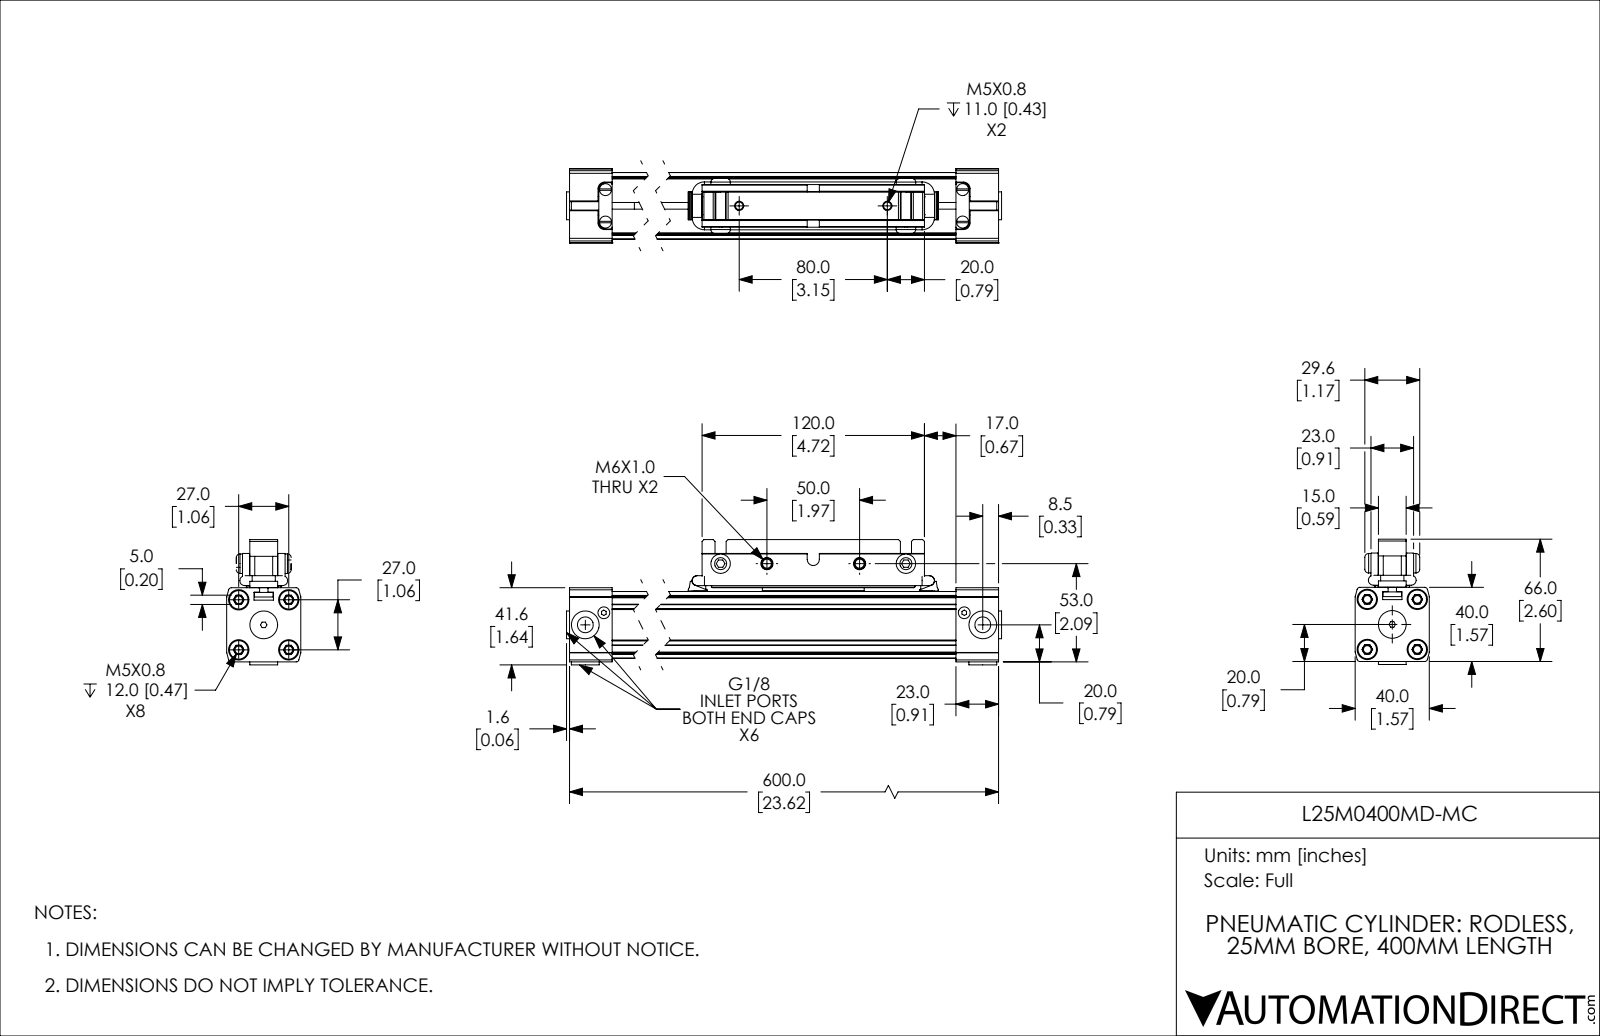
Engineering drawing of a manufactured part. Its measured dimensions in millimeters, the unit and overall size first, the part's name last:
Units: millimetres
Overall size (bounding box): 603.3 × 67.6 × 40
Round holes (diameter × count): ⌀4.1 ×6, ⌀8.6 ×5, ⌀15 ×5, ⌀6.5 ×4, ⌀6.6 ×4, ⌀11 ×4, ⌀4.9 ×2, ⌀4.9 ×2, ⌀6.4 ×2, ⌀25.1 ×1
Round bosses / shafts (diameter × count): ⌀10 ×4, ⌀9.7 ×3, ⌀8.2 ×3, ⌀10.5 ×2, ⌀5.3 ×2, ⌀5.3 ×2, ⌀25 ×1
Partial cylindrical surfaces — rounded edges, fillets, slot ends (radius × count): R0.3 ×28, R0.5 ×14, R1 ×14, R0.3 ×12, R3.5 ×8, R0.6 ×6, R1.5 ×6, R2.4 ×6
Main face-to-face distances: 35.9, 36, 10.9, 2, 8.5, 23, 38, 16.1, 19.7, 5.7
Hole centre spacings: 14, 19.1, 27, 572.2, 11.9, 17.5, 17.7, 20.5
Volume: 598 300 mm³ · Surface area: 210 500 mm²
Bodies: 13 solids, 883 faces (453 planar, 322 cylindrical, 108 other)
Part name (STEP PRODUCT): L25M0400MD-MC_BODY; L25M0400MD-MC; L25M0400MD-MC_PISTON
STEP written by: SolidWorks 2019 (CONFIG_CONTROL_DESIGN)
